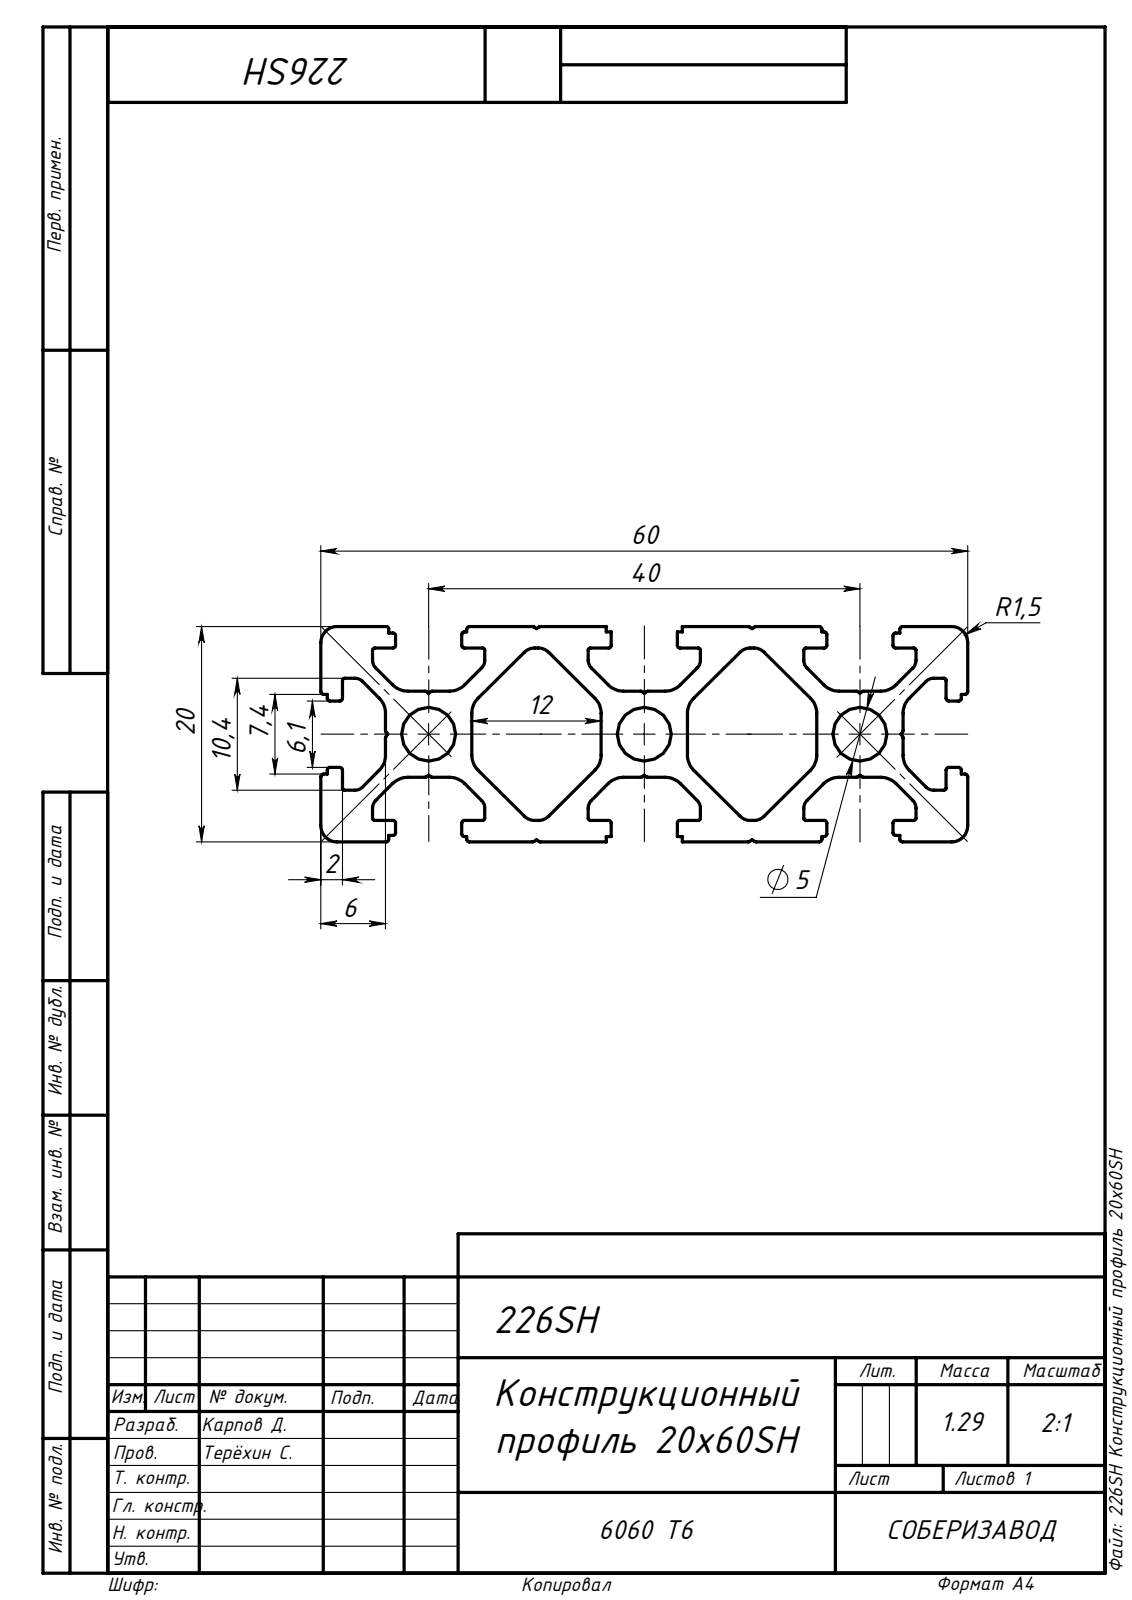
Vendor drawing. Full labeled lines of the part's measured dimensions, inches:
STEP written by: SolidWorks 2018 (AUTOMOTIVE_DESIGN)
Units: inches
Bodies: 1 solid, 308 faces (170 planar, 138 cylindrical, 0 other)
Overall size (bounding box): 39.37 × 2.362 × 0.787
Volume: 29.23 in³ · Surface area: 661.5 in²
Round holes (diameter × count): ⌀0.197 ×3
Partial cylindrical surfaces — rounded edges, fillets, slot ends (radius × count): R0.01 ×64, R0.079 ×24, R0.008 ×16, R0.039 ×16, R0.055 ×8, R0.059 ×4
Main face-to-face distances: 0.787, 0.472, 0.079, 0.551, 0.236, 0.157, 0.069, 0.487, 0.555, 0.709
Hole centre spacings: 0.787, 1.575
